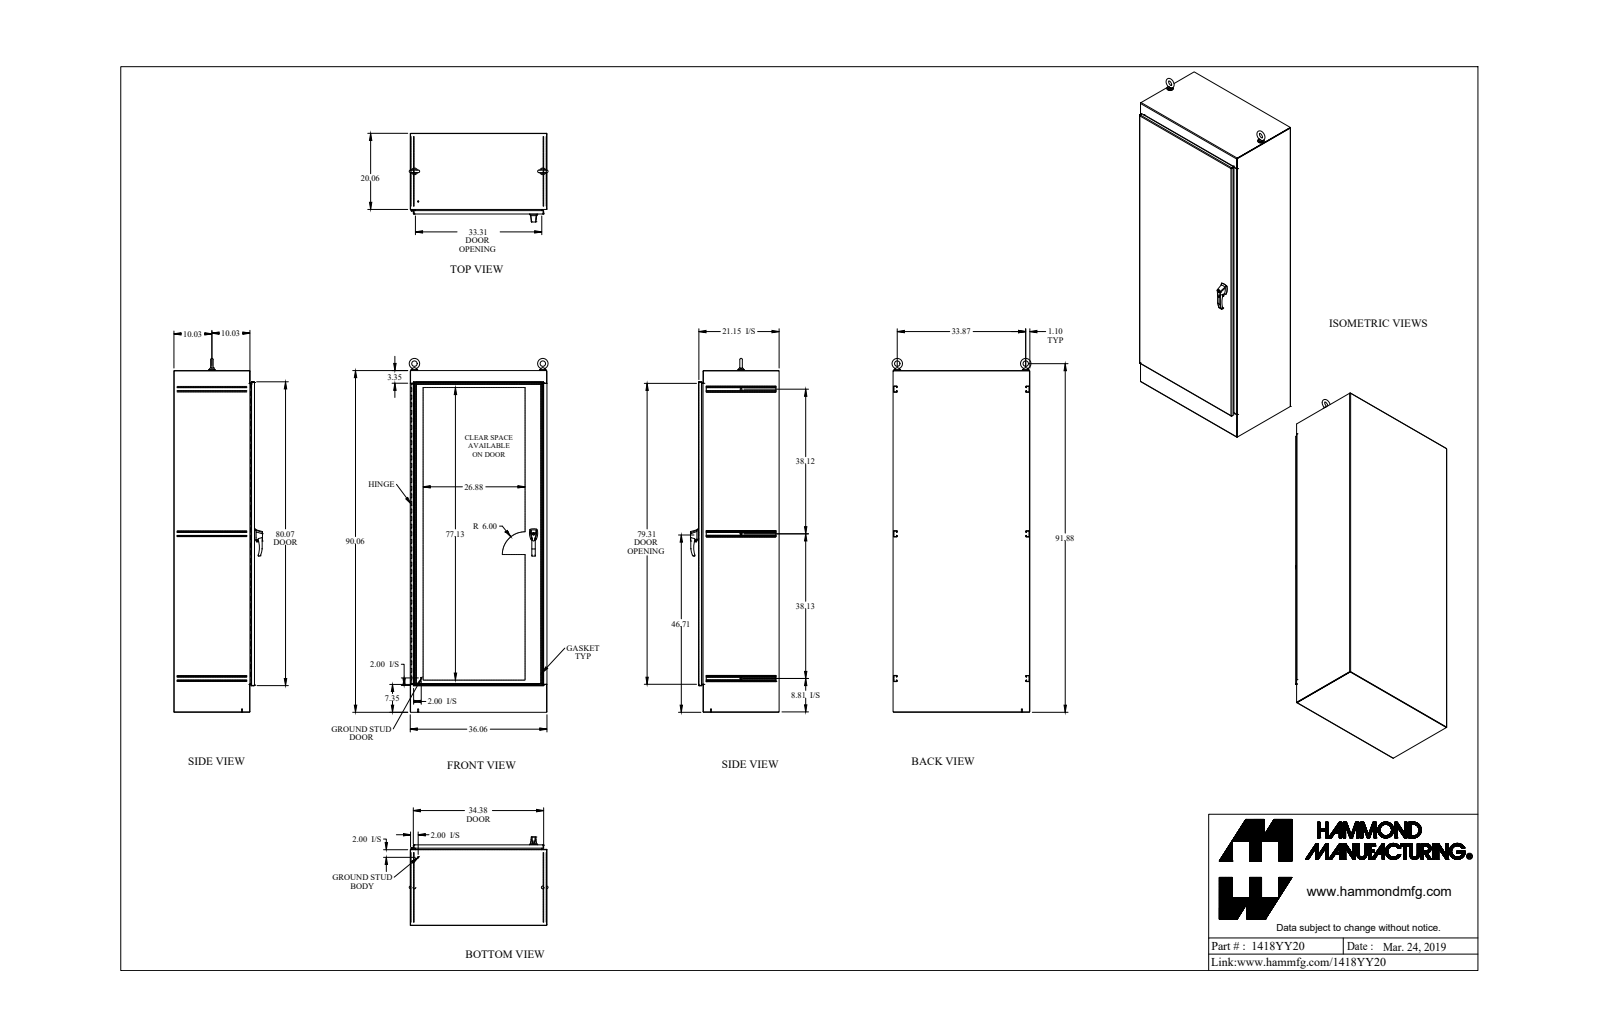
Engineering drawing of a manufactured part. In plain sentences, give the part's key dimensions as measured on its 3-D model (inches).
The part is named "1418YY20_Default". Its 3-D file was written by "SolidWorks 2019 (CONFIG_CONTROL_DESIGN)". It is 54 solids with 2644 faces: 1136 planar, 1343 cylindrical and 165 other. Overall it measures 93.713 by 37.119 by 23.362 inches. Its volume is 1 270 cubic inches and its surface area 26 862 square inches. Round holes: 14 of diameter 0.304, 6 of diameter 0.5, 2 of diameter 0.25, 2 of diameter 0.257, 2 of diameter 0.28, 2 of diameter 0.281, 2 of diameter 0.313, 2 of diameter 0.39, 2 of diameter 0.413, 2 of diameter 0.527, 2 of diameter 0.625, 2 of diameter 0.687. Round bosses or shafts: 4 of diameter 0.281, 2 of diameter 1.75, 2 of diameter 1.5, 2 of diameter 1.25, 2 of diameter 1, 2 of diameter 0.75, 2 of diameter 0.738, 2 of diameter 0.63. Partial cylindrical surfaces (rounded edges, fillets, slot ends): 42 of radius 0.043, 36 of radius 0.138, 22 of radius 0.125, 16 of radius 0.018, 13 of radius 0.048, 13 of radius 0.143, 10 of radius 0.06, 8 of radius 0.015. The main face-to-face distances are 0.095, 21.152, 35.965, 21.057, 21.247, 35.87, 36.06, 89.965, 1.187, 19.965. The hole center spacings are 6, 12, 18, 24, 30, 36, 42, 48.
